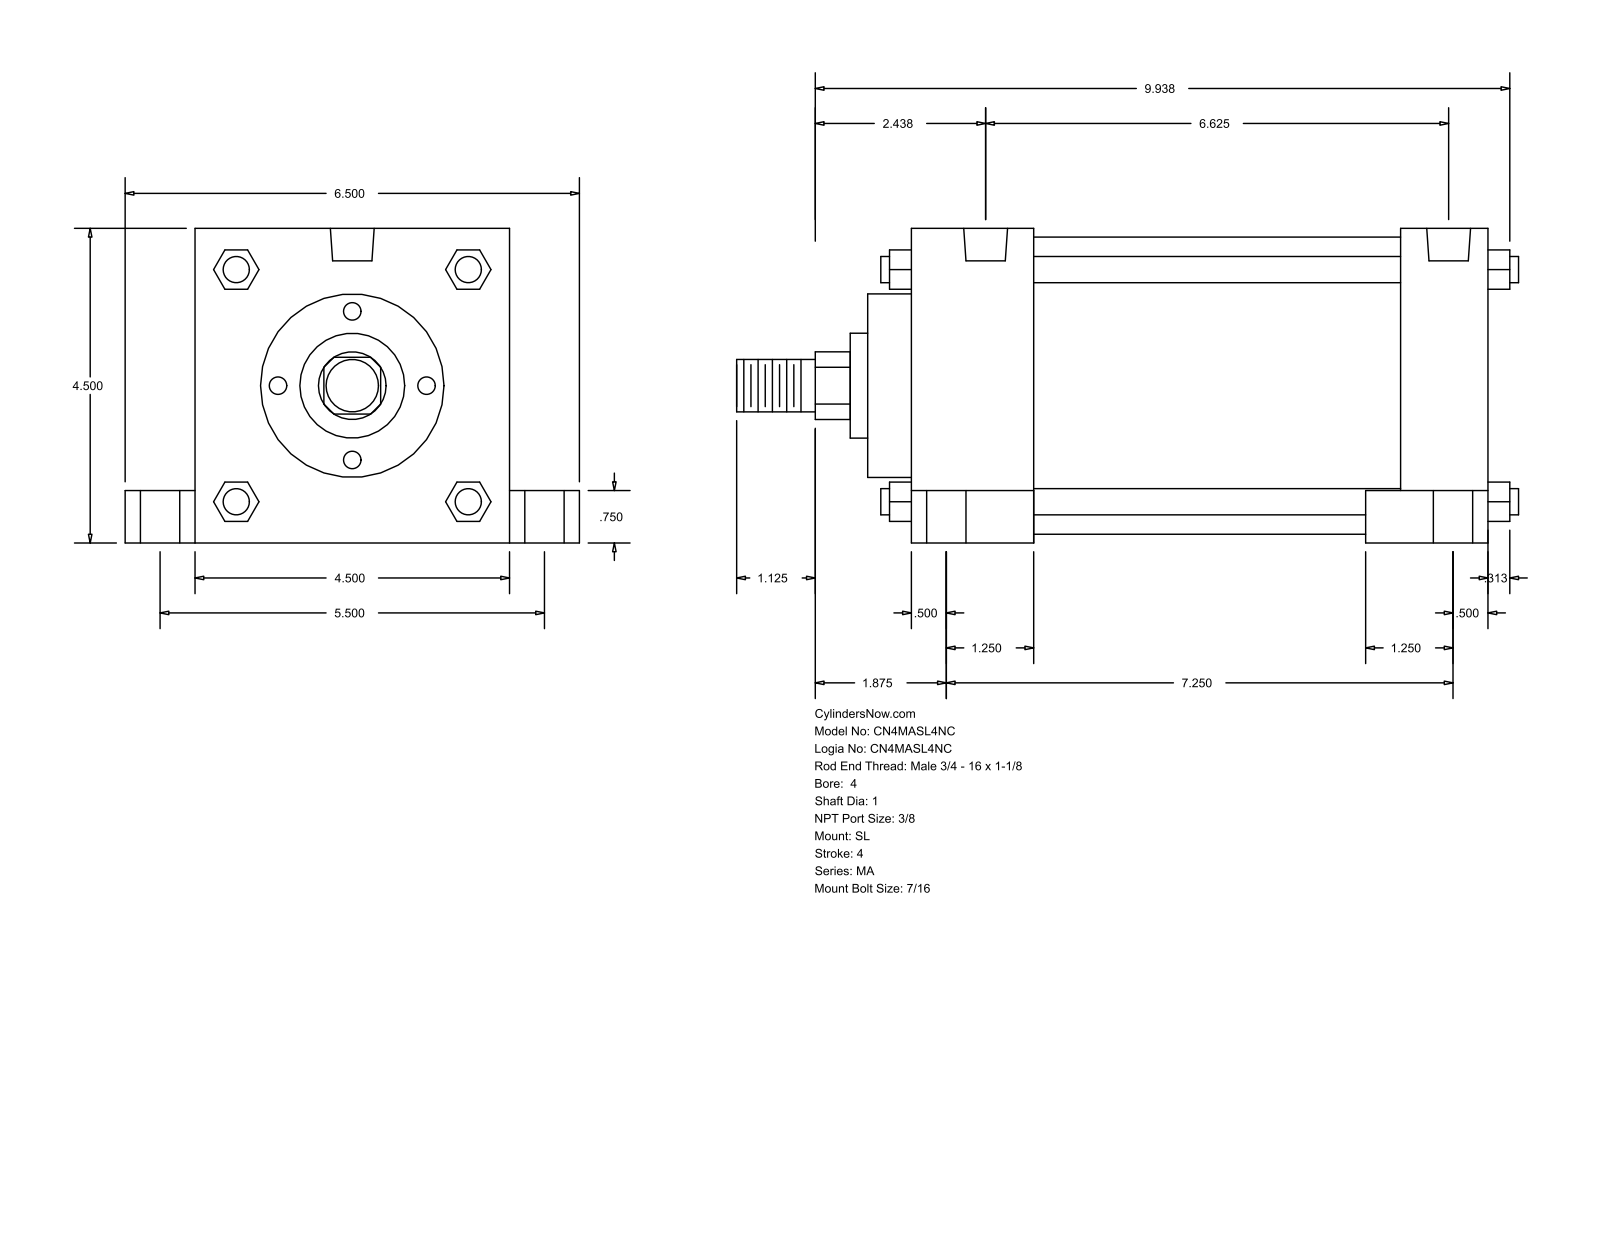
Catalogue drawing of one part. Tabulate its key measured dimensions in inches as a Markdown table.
| quantity | value |
| --- | --- |
| part name | MA_SL__0400_1 |
| STEP written by | GSSL Pune (CONFIG_CONTROL_DESIGN) |
| units | inches |
| bodies | 0 solids, 150 faces (113 planar, 37 cylindrical, 0 other) |
| overall size | 11.187 × 6.5 × 4.5 |
| round holes (diameter × count) | 0.437 × 4, 0.563 × 4, 0.813 × 4, 0.627 × 2 |
| round bosses / shafts (diameter × count) | 0.375 × 4, 4.25 × 1, 2.625 × 1, 1.5 × 1, 1 × 1, 0.75 × 1 |
| partial cylindrical surfaces (radius × count) | 0.484 × 1 |
| main face-to-face distances | 4.5, 8.25, 1.75, 6.5, 7, 5.25, 1.25, 1, 5.5, 8.875 |
| hole center spacings | 0.187, 2.751, 2.761, 2.807, 2.85, 5.5, 6.25, 6.438 |
